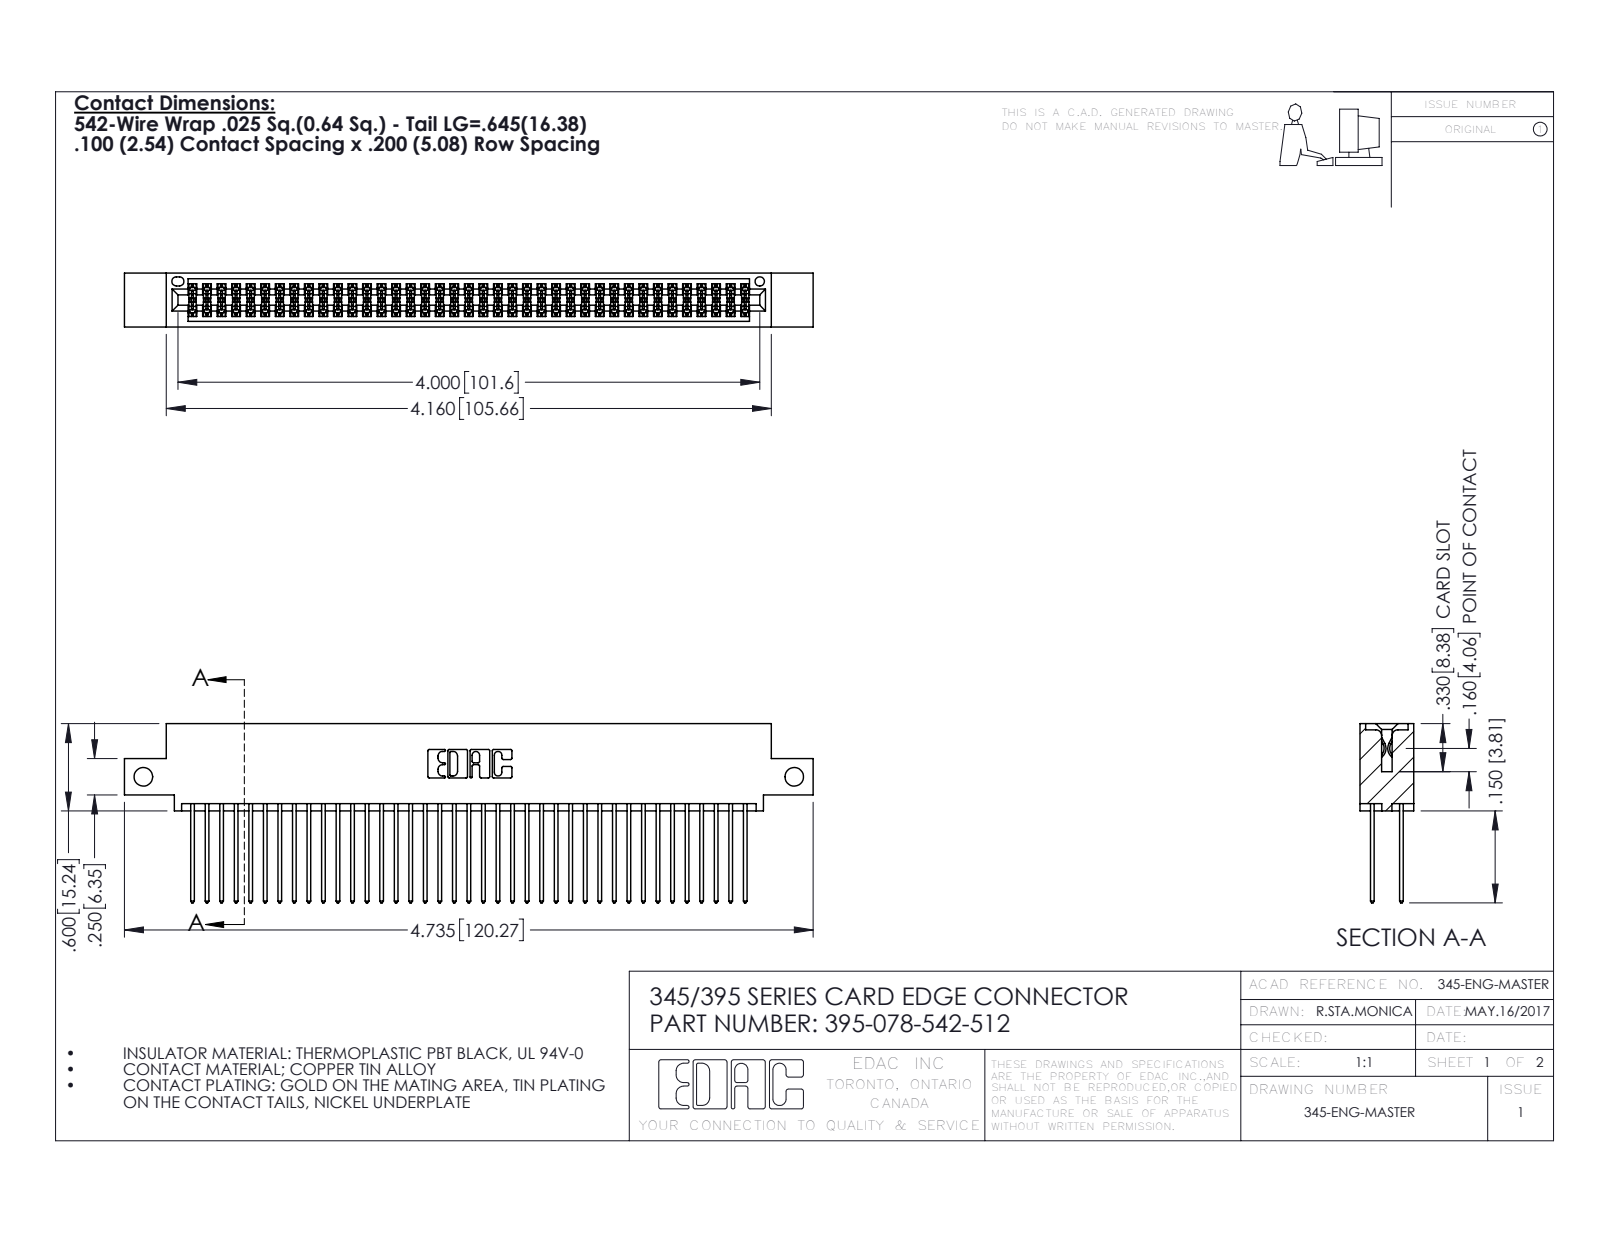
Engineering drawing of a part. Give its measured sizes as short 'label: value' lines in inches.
name: 345 Part_0.110 Offset - Side Mount; 395-078-542-512; 345-292-001_345-293-142
written by: SolidWorks 2016 (CONFIG_CONTROL_DESIGN)
unit: in
bodies: 79 solids, 4030 faces (2658 planar, 1372 cylindrical, 0 other)
size: 4.735 × 1.232 × 0.37
volume: 0.724 in³; area: 29.65 in²
holes: 2× ⌀0.128, 1× ⌀0.064
rounds: 117× R0.006, 78× R0.01, 22× R0.01, 6× R0.007, 6× R0.031, 3× R0.026, 2× R0.014, 2× R0.019
face distances: 0.298, 0.072, 0.2, 0.098, 0.272, 0.025, 0.225, 0.37, 0.175, 0.149
hole spacings: 4.475
